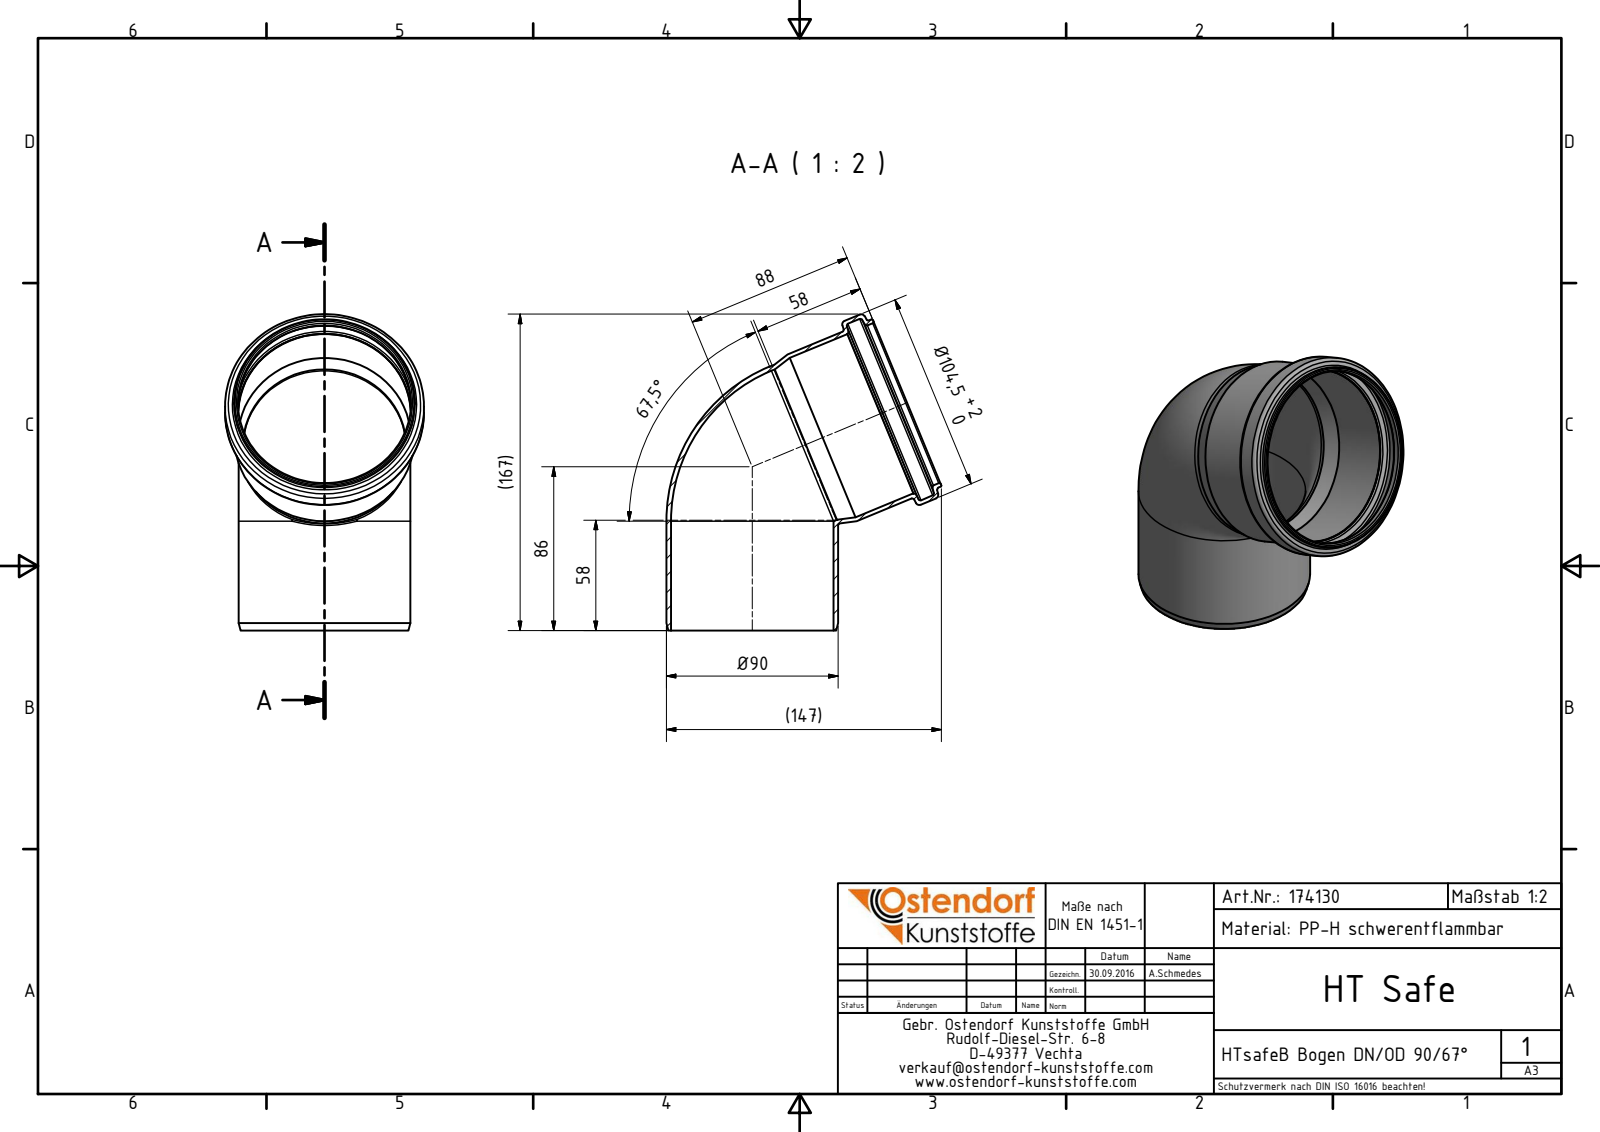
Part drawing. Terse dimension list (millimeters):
name: 174130 HTsafeB DN_OD 90_67°
written by: Autodesk Inventor 2016 (AUTOMOTIVE_DESIGN)
unit: mm
bodies: 1 solid, 35 faces (4 planar, 11 cylindrical, 20 other)
size: 166.11 × 144.43 × 104.5
volume: 101 994 mm³; area: 99 898 mm²
holes: 2× ⌀85.44, 2× ⌀90.8, 1× ⌀90.5, 1× ⌀100.3
bosses: 2× ⌀90.2, 1× ⌀104.5, 1× ⌀95, 1× ⌀94.7
face distances: 15.21, 42.32, 57.53
